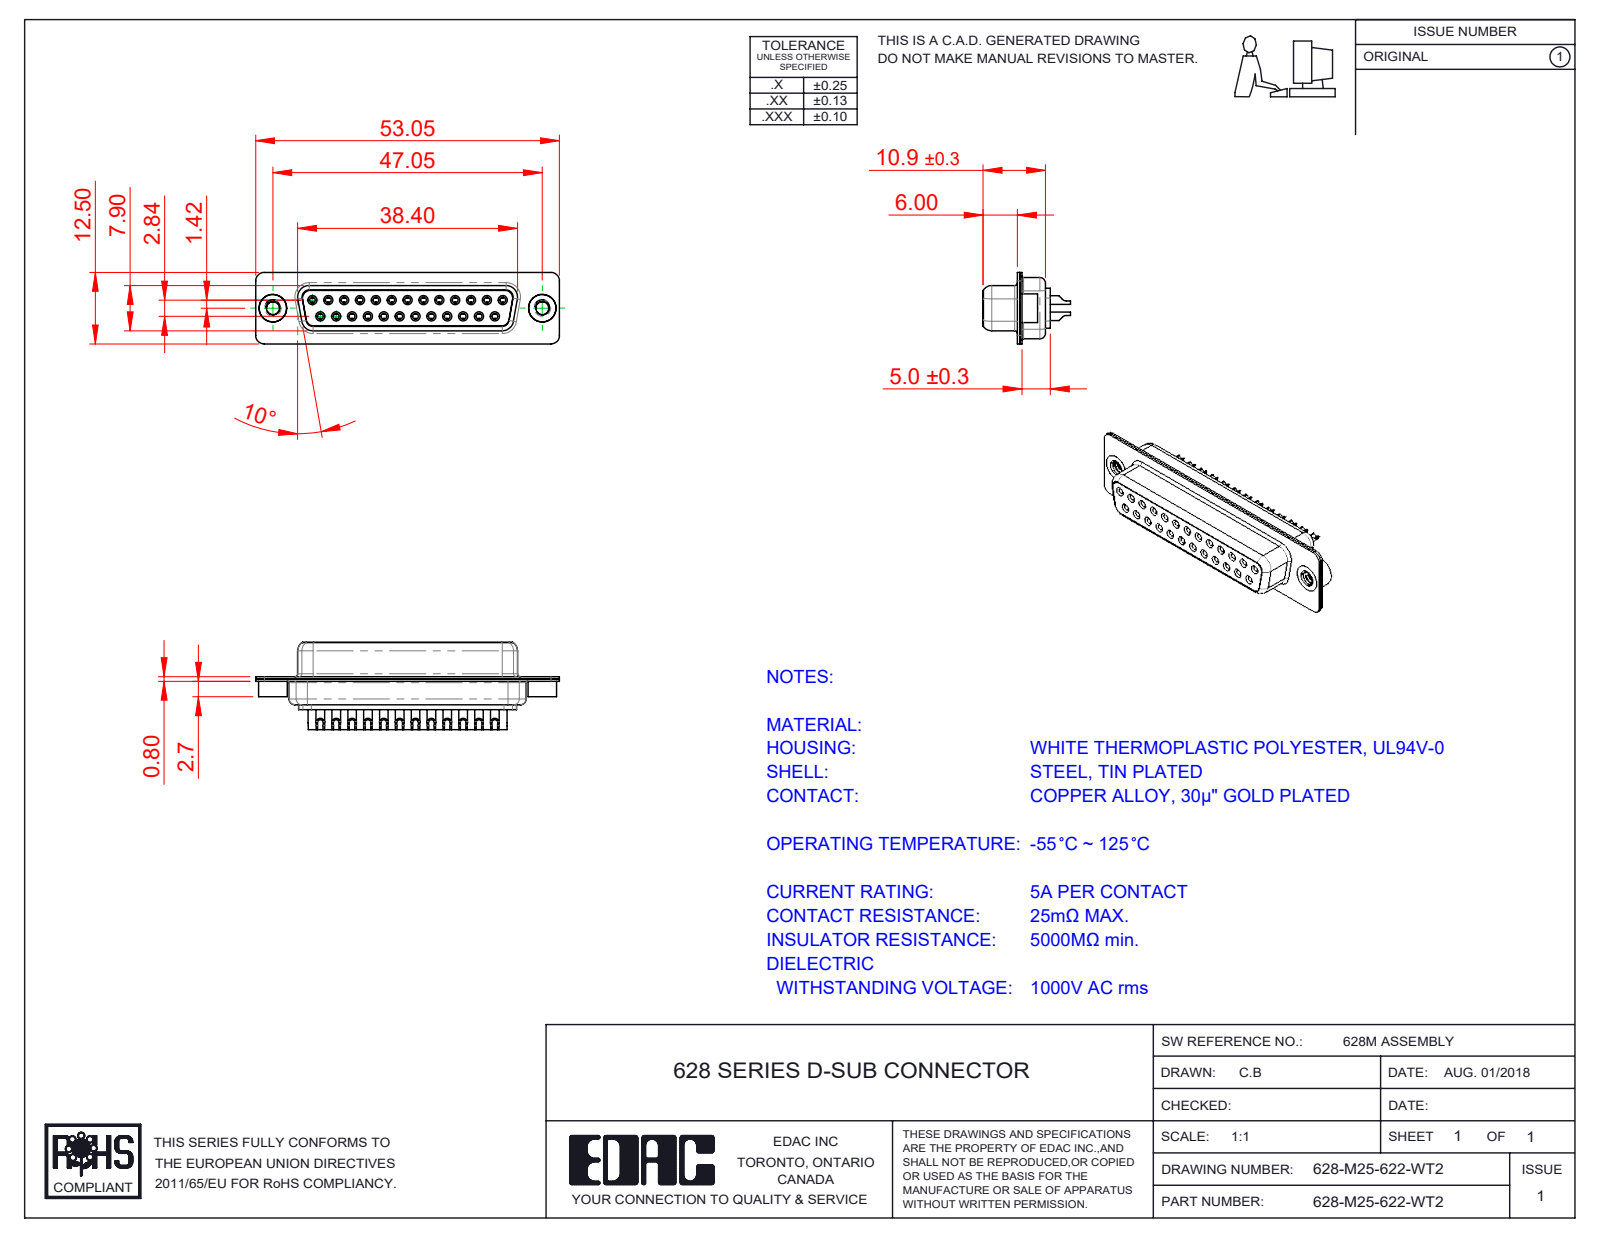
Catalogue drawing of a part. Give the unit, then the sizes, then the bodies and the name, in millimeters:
Units: millimetres
Overall size (bounding box): 53.05 × 15.25 × 12.5
Round holes (diameter × count): ⌀1 ×25, ⌀1.1 ×25, ⌀1.7 ×25, ⌀1.8 ×25, ⌀2 ×25, ⌀2.26 ×2, ⌀4 ×2, ⌀4.8 ×2
Round bosses / shafts (diameter × count): ⌀2.2 ×25, ⌀1.6 ×25, ⌀1.5 ×25, ⌀5 ×2, ⌀4.9 ×2
Partial cylindrical surfaces — rounded edges, fillets, slot ends (radius × count): R1.5 ×16, R2 ×12, R1.35 ×8, R1.6 ×8, R1 ×6, R0.25 ×4, R0.5 ×4, R0.6 ×4
Main face-to-face distances: 0.4, 1.4, 0.45, 8.45, 8.9, 1.8, 7.05, 0.85, 1, 1.85
Hole centre spacings: 3.16, 2.77, 5.54, 8.31, 11.08, 13.85, 5.04, 7.49
Volume: 3 776 mm³ · Surface area: 9 354 mm²
Bodies: 30 solids, 1655 faces (493 planar, 662 cylindrical, 500 other)
Part name (STEP PRODUCT): 628M Contact Row 1_22; 628-M25-622-WT2; 628M Contact Row 2_22; 628M Shell Front_25 Contacts (+3 more)
STEP written by: SolidWorks 2020 (CONFIG_CONTROL_DESIGN)
